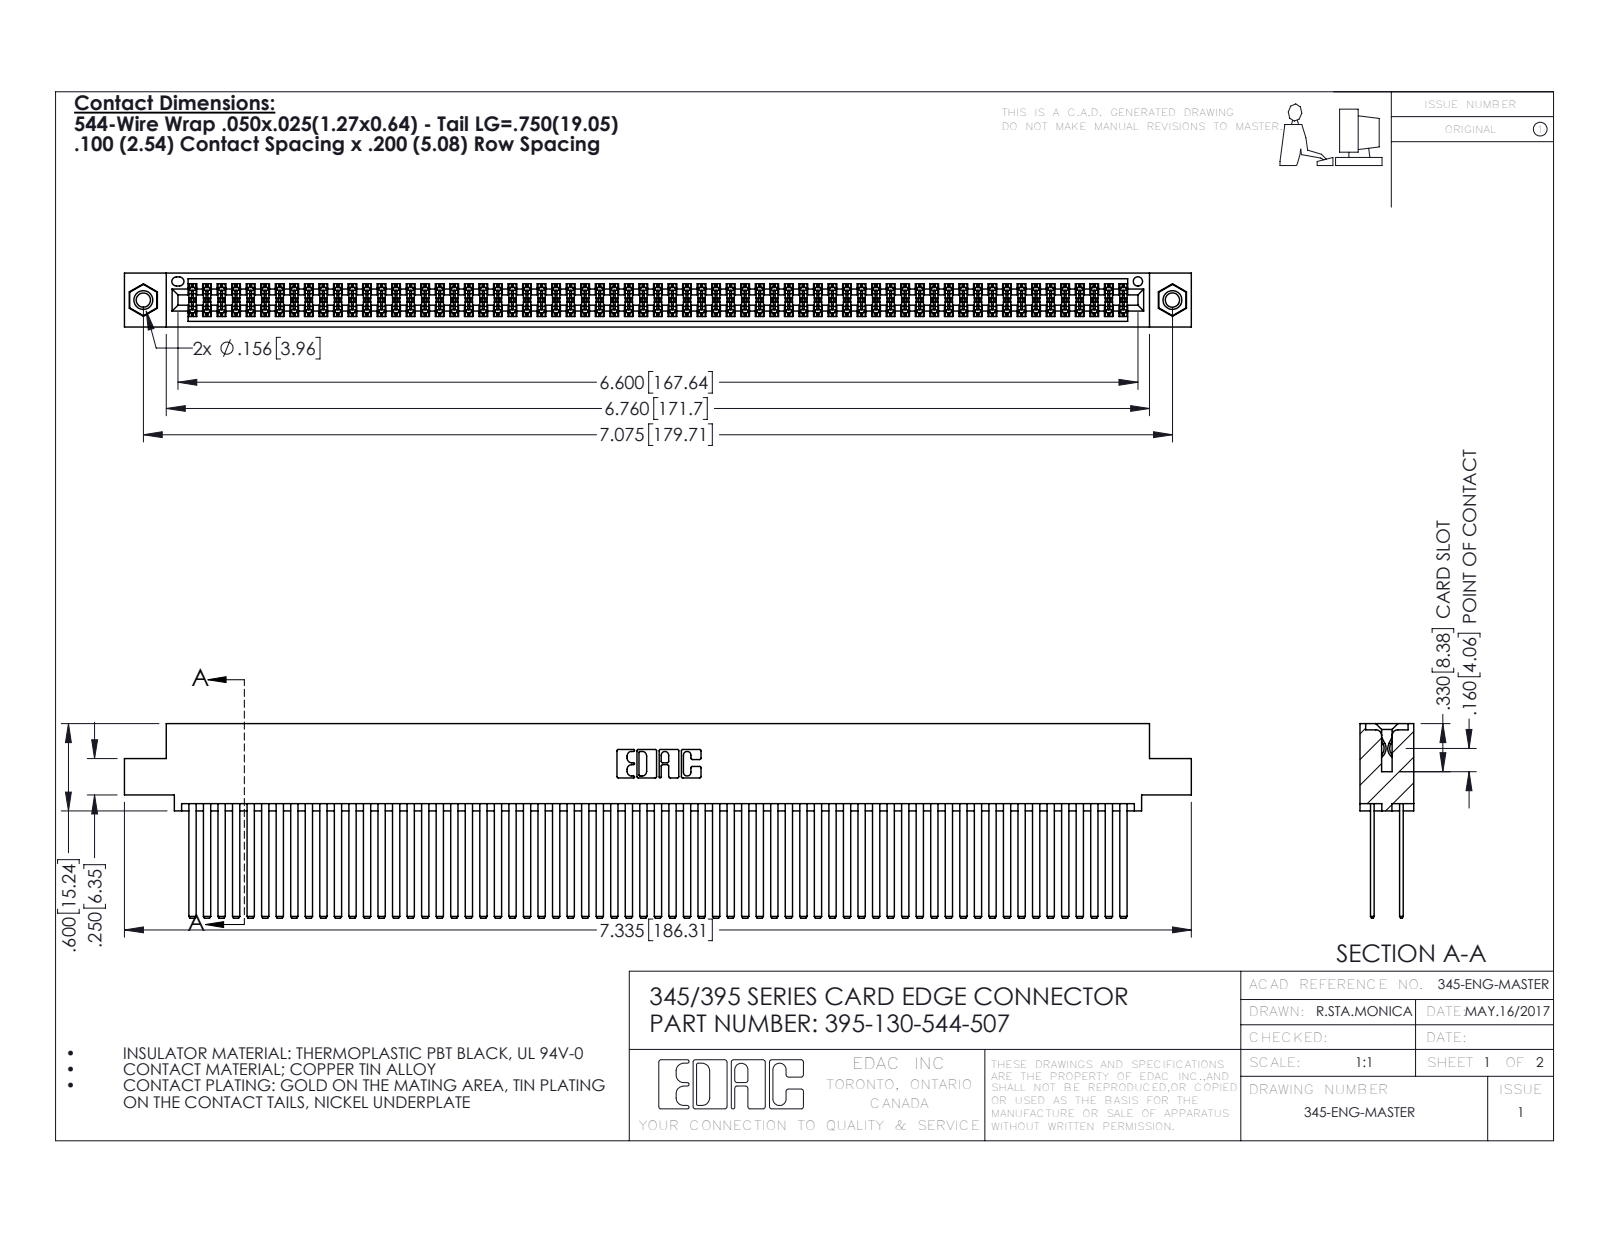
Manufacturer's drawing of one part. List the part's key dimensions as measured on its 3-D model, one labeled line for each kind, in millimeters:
Part name (STEP PRODUCT): 345-292-001_345-293-144; 345-250-001_345-250-005-103; 345 Part_0.110 Offset - 0.156 Dia-TI; 395-130-544-507
STEP written by: SolidWorks 2016 (CONFIG_CONTROL_DESIGN)
Units: millimetres
Bodies: 133 solids, 5910 faces (3886 planar, 2008 cylindrical, 16 other)
Overall size (bounding box): 186.3 × 34 × 9.4
Volume: 20 040 mm³ · Surface area: 35 540 mm²
Round holes (diameter × count): ⌀2.5 ×2, ⌀3.2 ×2, ⌀4 ×2, ⌀1.6 ×1
Round bosses / shafts (diameter × count): ⌀3.9 ×2
Partial cylindrical surfaces — rounded edges, fillets, slot ends (radius × count): R0.2 ×195, R0.3 ×22, R0.2 ×6, R0.8 ×6, R0.7 ×3, R0.4 ×2, R0.5 ×2, R0.6 ×2
Main face-to-face distances: 5.1, 0.6, 1.8, 2.5, 6.9, 7.6, 5.7, 4.4, 9.4, 3.8
Hole centre spacings: 6.9, 173.7, 179.7
